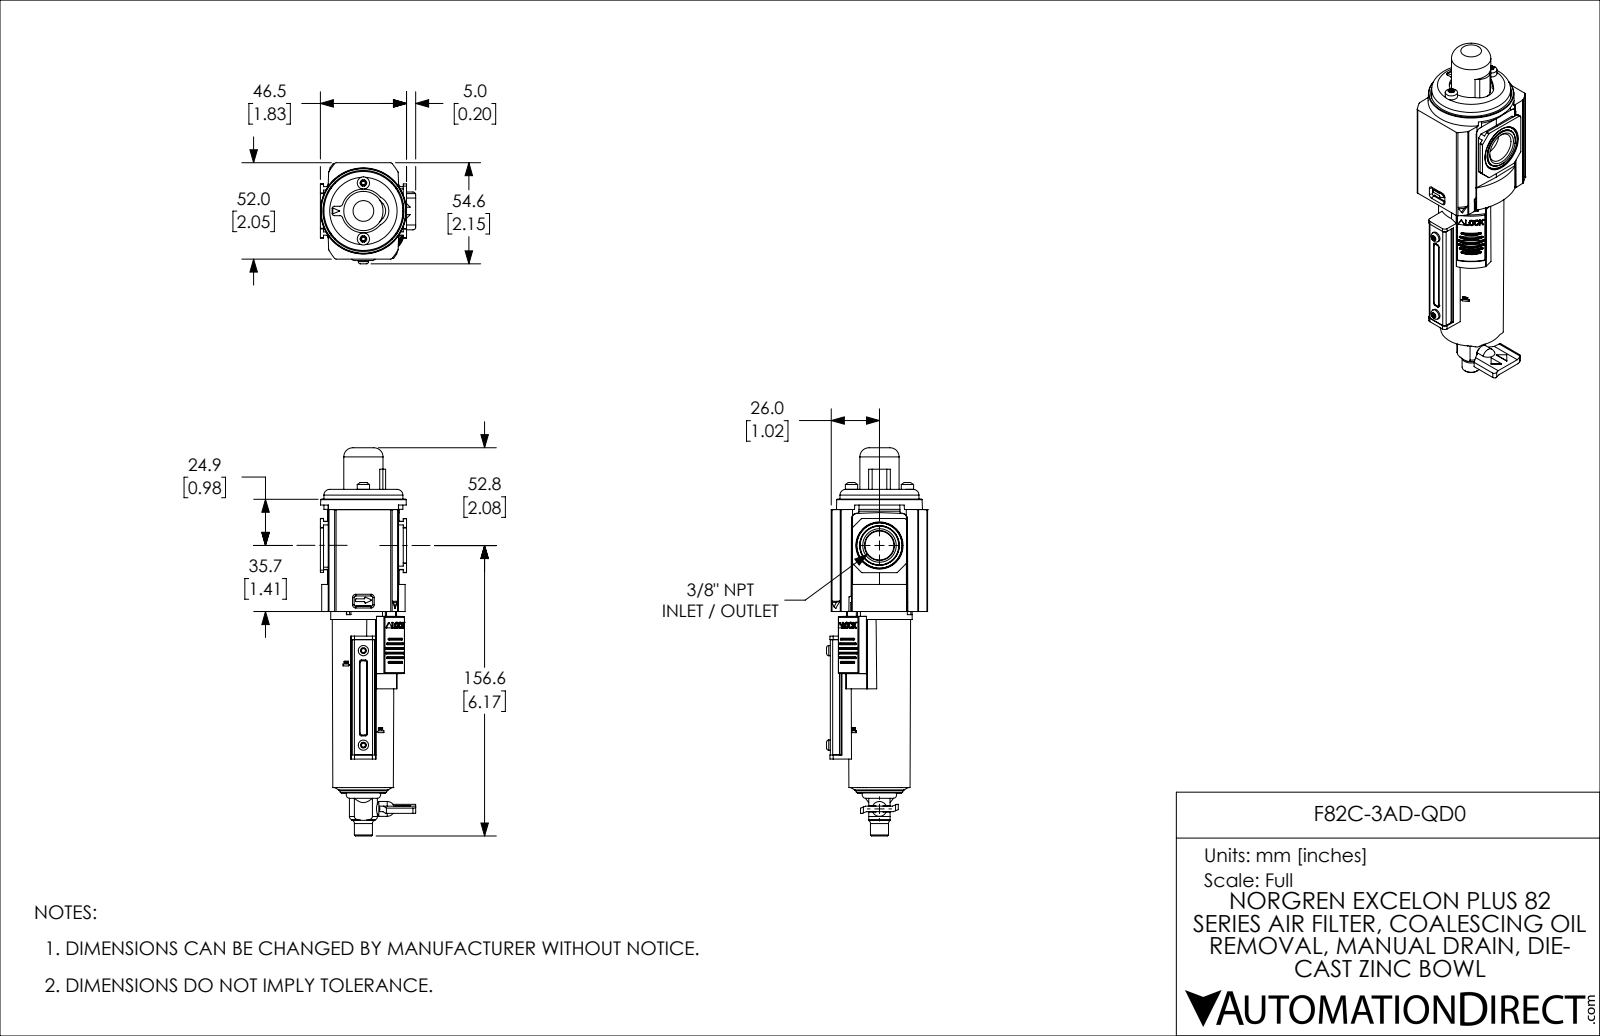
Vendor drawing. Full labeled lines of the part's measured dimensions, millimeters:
Part name (STEP PRODUCT): F82C-3AD-QD0
STEP written by: SolidWorks 2021 (CONFIG_CONTROL_DESIGN)
Units: millimetres
Bodies: 8 solids, 1211 faces (526 planar, 481 cylindrical, 204 other)
Overall size (bounding box): 209.4 × 54.6 × 51.5
Volume: 230 400 mm³ · Surface area: 62 560 mm²
Round holes (diameter × count): ⌀1.5 ×2, ⌀2 ×2, ⌀3.3 ×2, ⌀4.4 ×2, ⌀6.4 ×1, ⌀16 ×1
Round bosses / shafts (diameter × count): ⌀6.6 ×2, ⌀5.5 ×2, ⌀4 ×2, ⌀42.6 ×1, ⌀38.7 ×1, ⌀35.3 ×1, ⌀34.4 ×1, ⌀32.8 ×1
Partial cylindrical surfaces — rounded edges, fillets, slot ends (radius × count): R0.5 ×73, R1 ×38, R0.3 ×12, R0.5 ×12, R0.3 ×10, R0.8 ×8, R0.9 ×8, R1.2 ×8
Main face-to-face distances: 1.5, 50.5, 52, 49, 48.2, 4.6, 34.3, 37.5, 3.1, 6
Hole centre spacings: 20.2, 13.5, 15.1, 15.1, 30.2, 27, 30.2, 30.2
